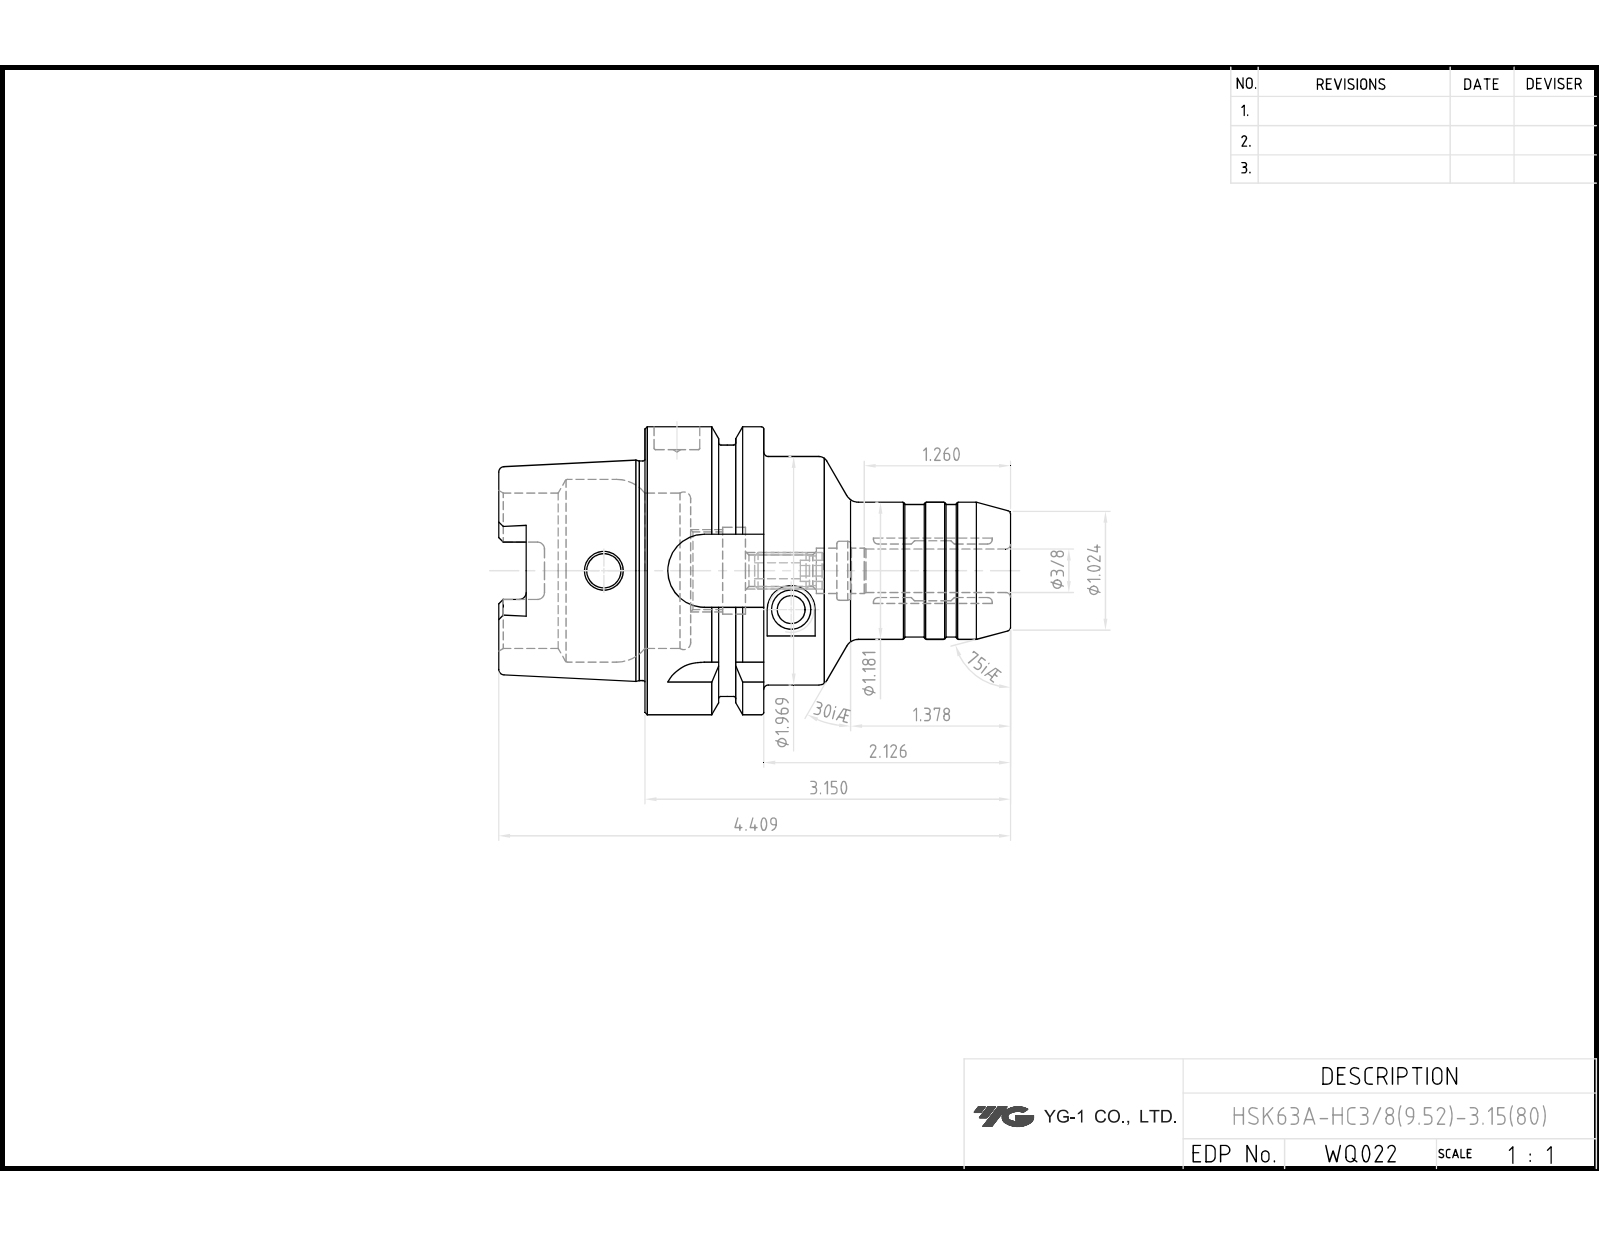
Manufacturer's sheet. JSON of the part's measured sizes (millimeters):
{"part_name": "LO-HSK63A-HC6_35-70", "step_written_by": "CREO PARAMETRIC BY PTC INC, 2018500 (CONFIG_CONTROL_DESIGN)", "units": "millimeters", "bodies": {"solids": 1, "faces": 207, "planar": 56, "cylindrical": 59, "other": 92}, "overall_size": [112, 63, 63], "volume_mm3": 134768, "surface_area_mm2": 29658, "round_holes": [[10, 2], [7.5, 1], [8, 1], [9.53, 1], [17, 1], [18, 1], [19, 1], [34, 1], [40, 1]], "round_bosses_or_shafts": [[63, 1], [55, 1], [50, 1], [48.04, 1], [30, 1], [29, 1]], "partial_cylinders_radius": [[1.5, 6], [2.88, 4], [8, 4]], "face_to_face_distances": [26, 54, 58, 10, 16, 32, 6.12, 9.88, 80, 70]}
